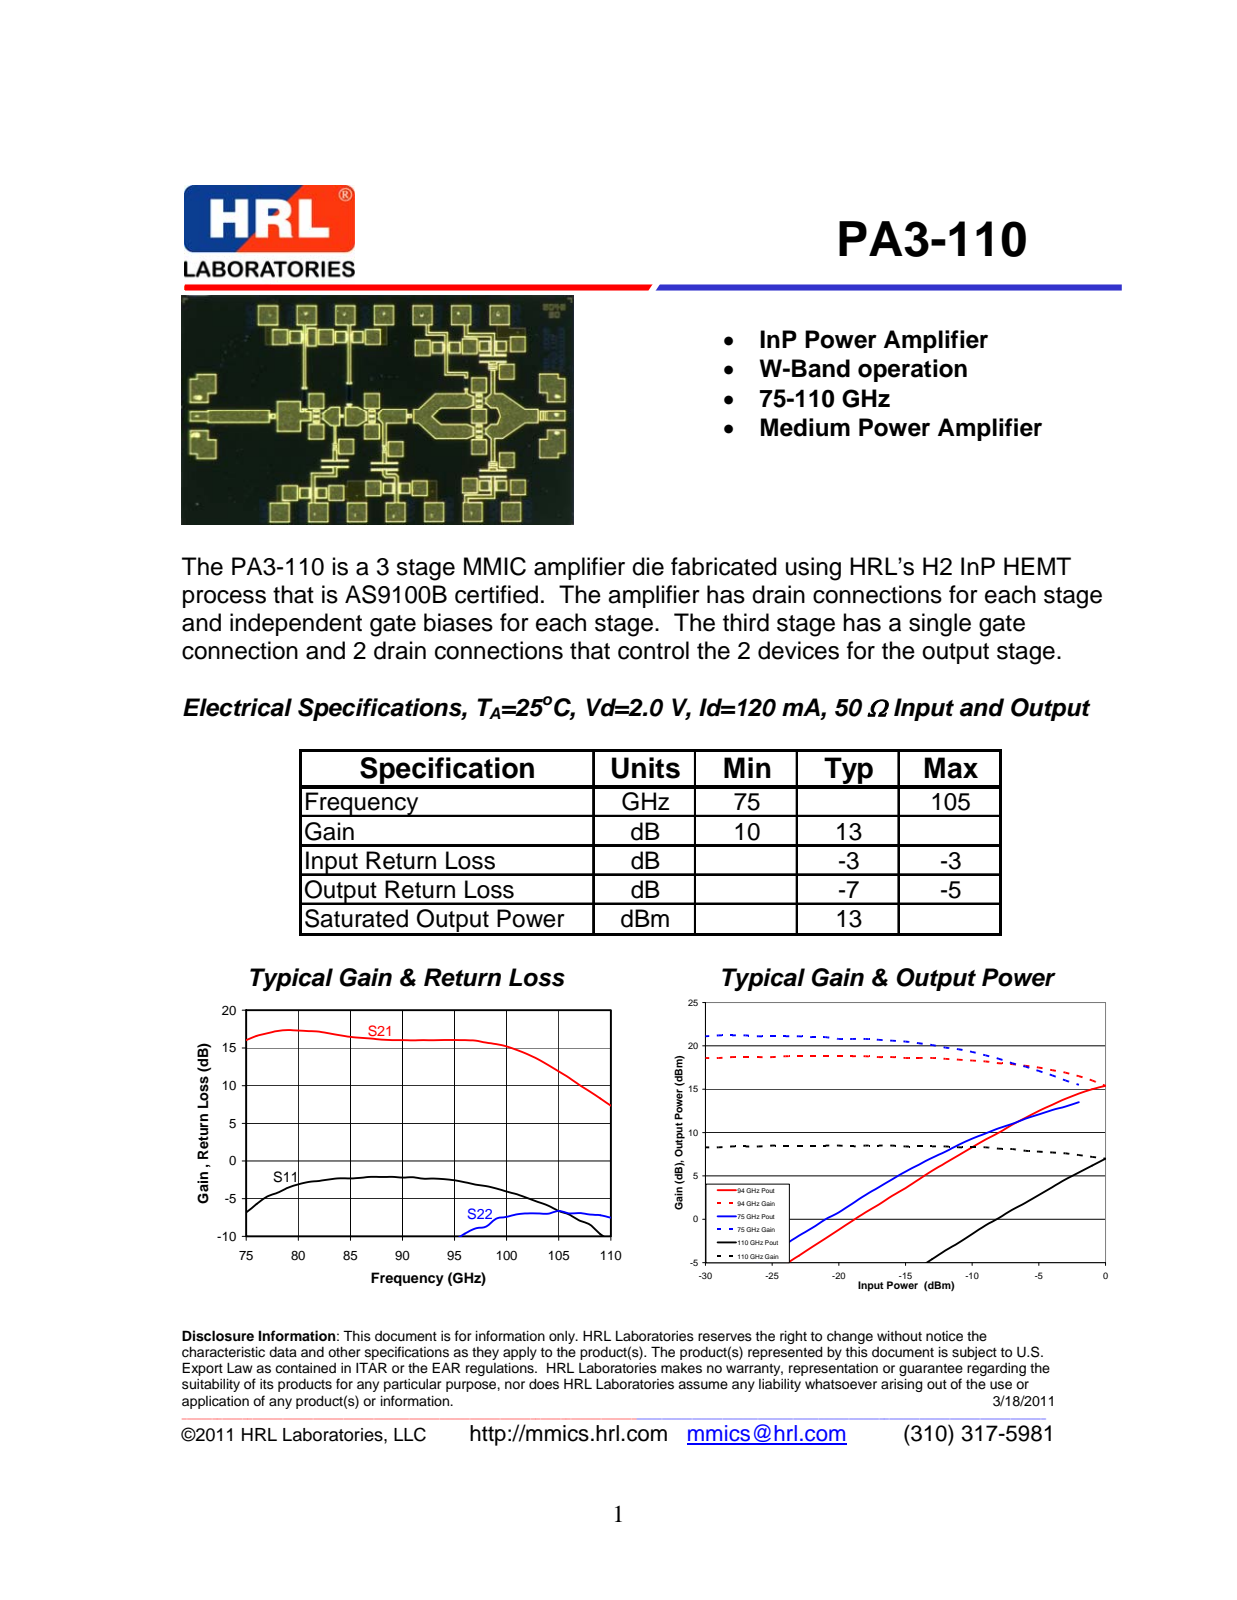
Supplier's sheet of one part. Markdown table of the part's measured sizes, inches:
| quantity | value |
| --- | --- |
| part name | PA3-110 |
| STEP written by | Autodesk Inventor 2010 (AUTOMOTIVE_DESIGN) |
| units | inches |
| bodies | 1 solid, 1366 faces (1366 planar, 0 cylindrical, 0 other) |
| overall size | 0.081 × 0.049 × 0.002 |
| main face-to-face distances | 0.049, 0.081, 0.043, 0.041, 0.047, 0.04, 0.041, 0.04, 0.039, 0.043 |
